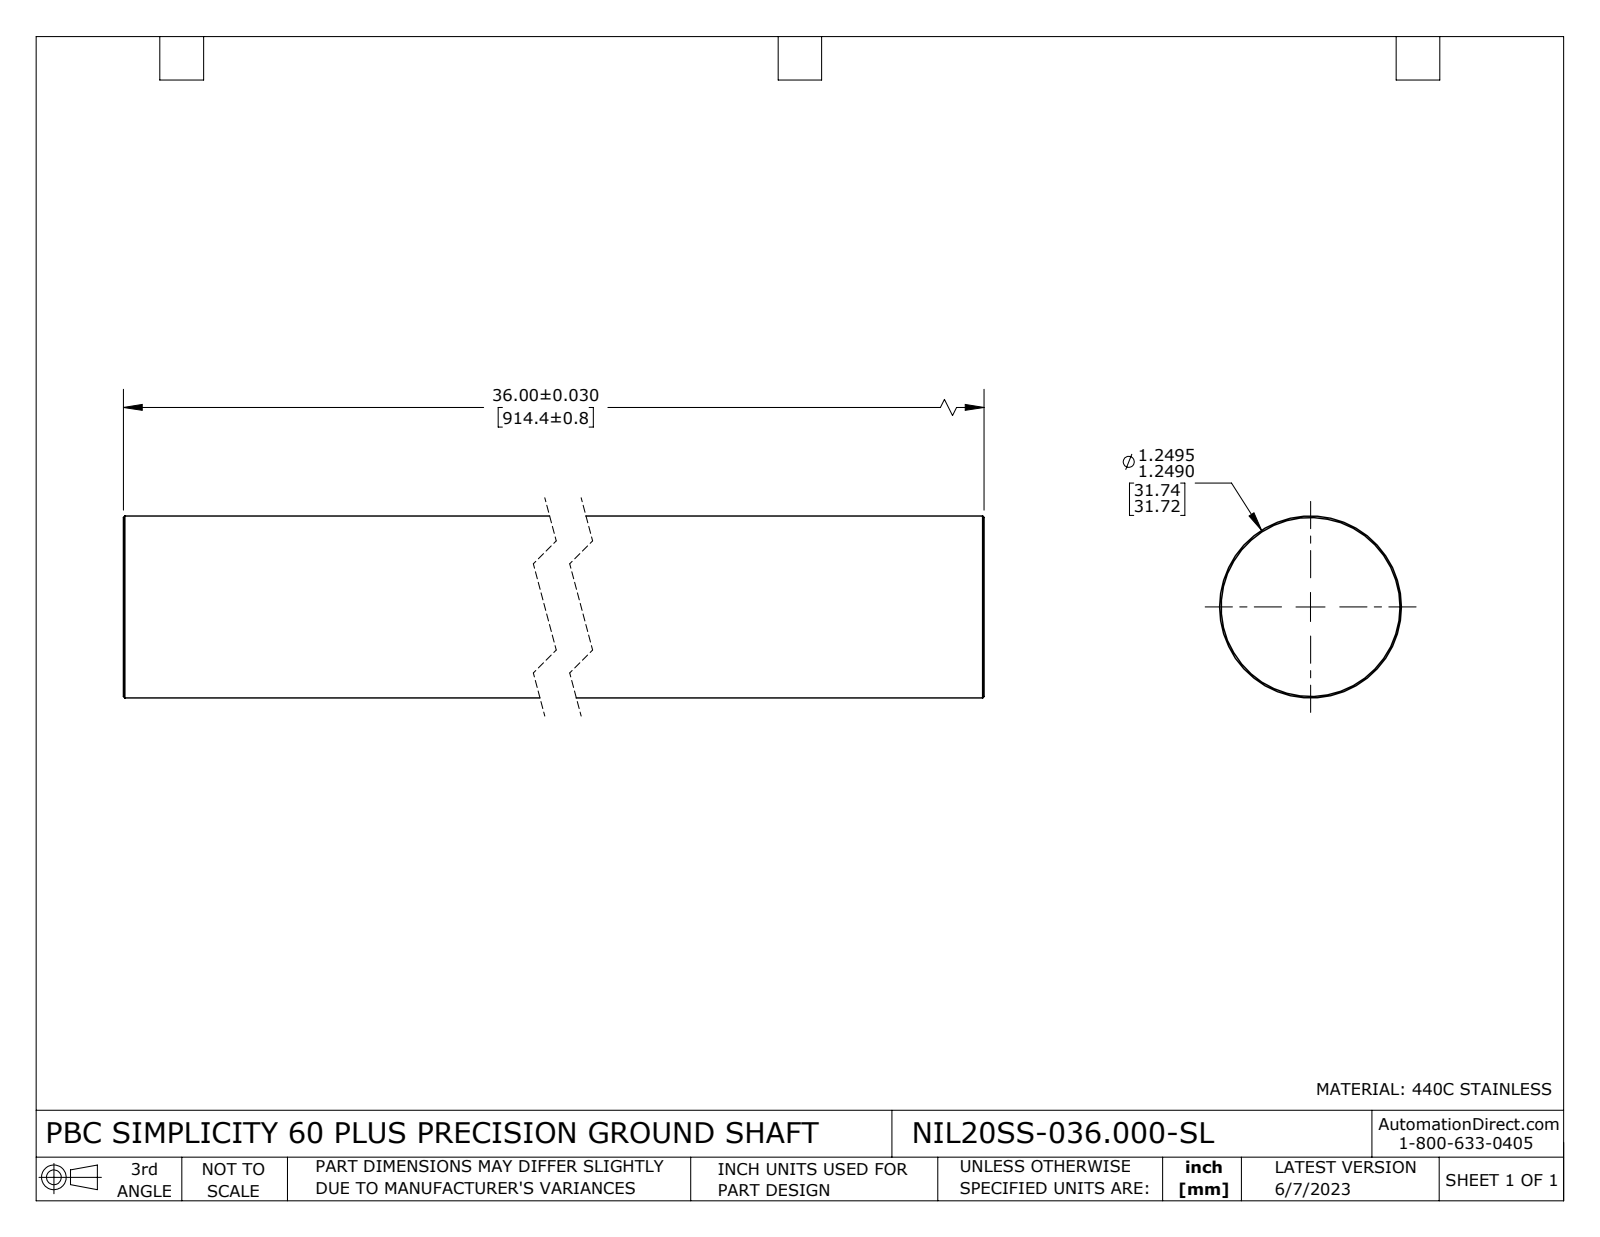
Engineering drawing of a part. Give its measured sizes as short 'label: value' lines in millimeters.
name: NIL20SS-036.000-SL
written by: SolidWorks 2021 (CONFIG_CONTROL_DESIGN)
unit: mm
bodies: 1 solid, 8 faces (2 planar, 2 cylindrical, 4 other)
size: 914.4 × 31.8 × 31.8
volume: 724 000 mm³; area: 92 770 mm²
bosses: 1× ⌀31.8
face distances: 914.4
